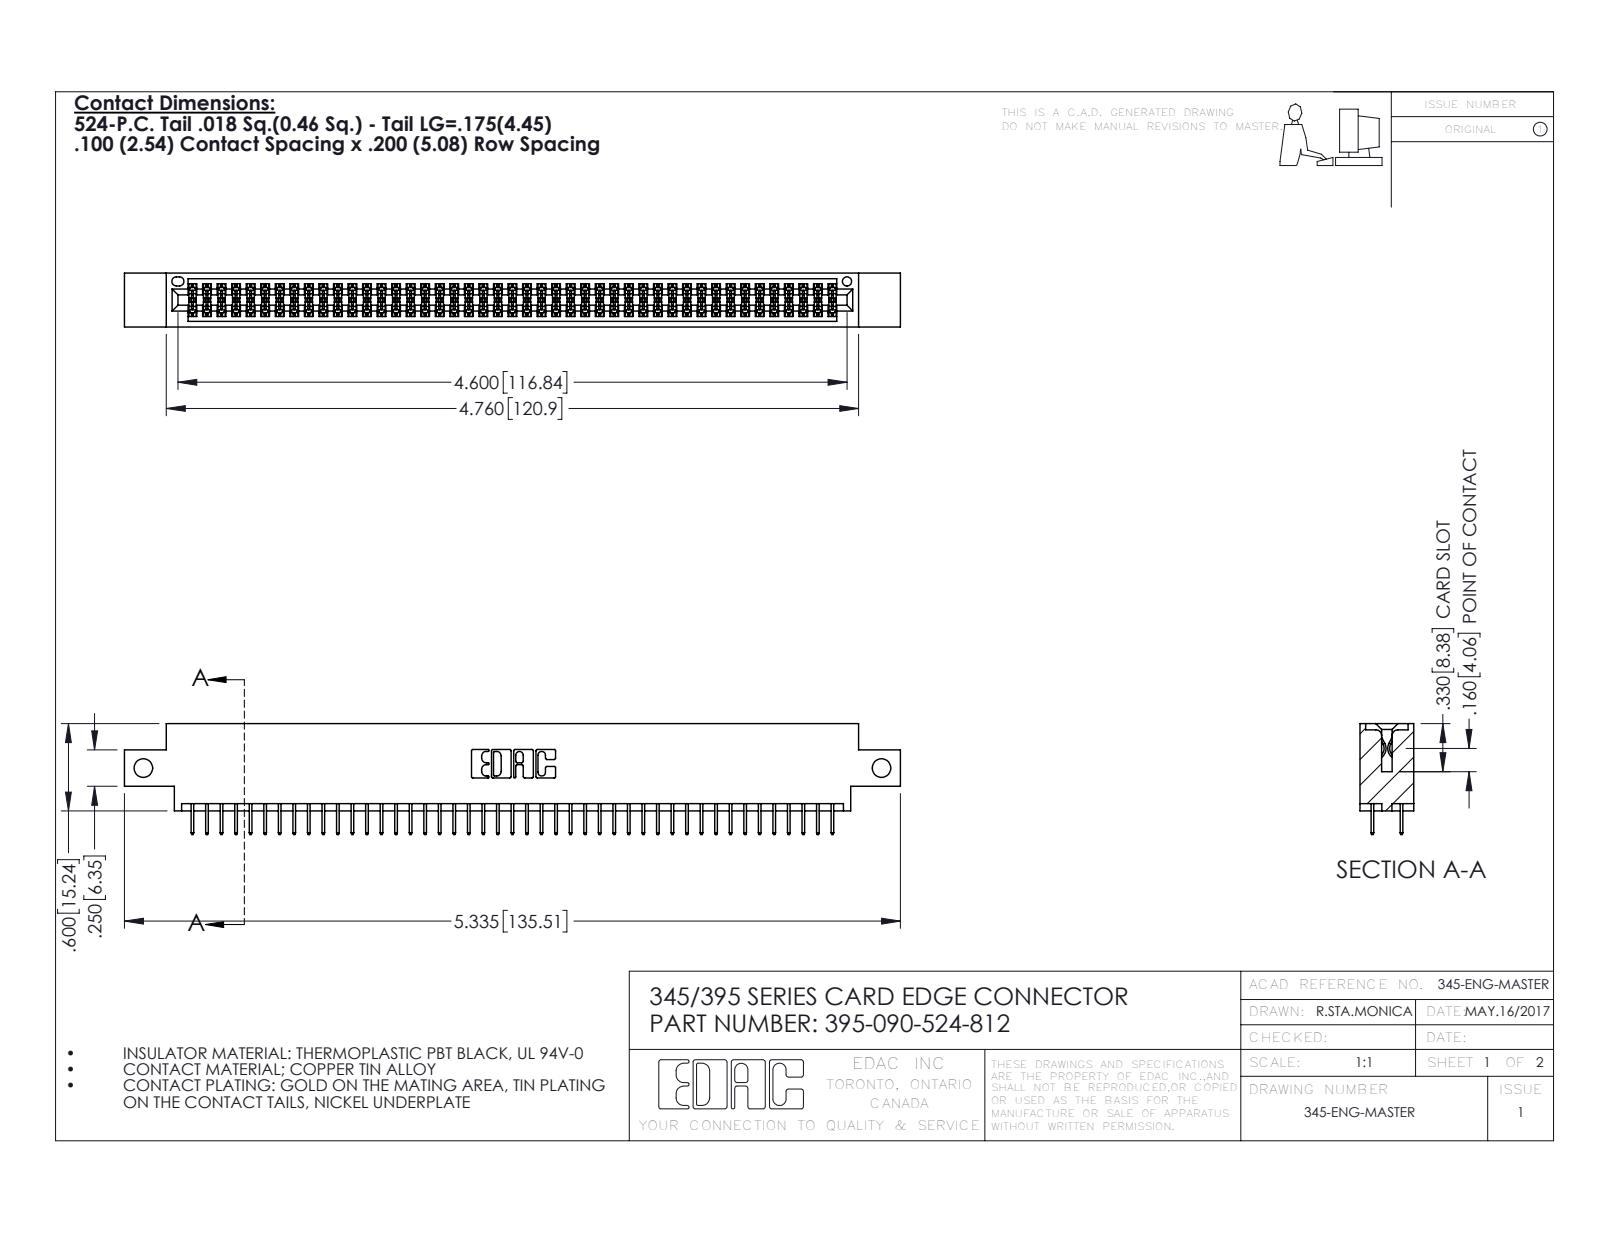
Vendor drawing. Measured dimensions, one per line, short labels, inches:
name: 345-292-001_345-293-124; 395-090-524-812; 345 Part_0.170 Offset - Side Mount
written by: SolidWorks 2016 (CONFIG_CONTROL_DESIGN)
unit: in
bodies: 91 solids, 4990 faces (3594 planar, 1396 cylindrical, 0 other)
size: 5.335 × 0.762 × 0.37
volume: 0.784 in³; area: 29 in²
holes: 2× ⌀0.128, 1× ⌀0.064
rounds: 135× R0.006, 22× R0.01, 6× R0.007, 6× R0.031, 3× R0.026, 2× R0.014, 2× R0.019, 2× R0.022
face distances: 0.072, 0.298, 0.37, 0.2, 0.098, 0.272, 0.025, 0.225, 0.175, 0.072
hole spacings: 5.075
